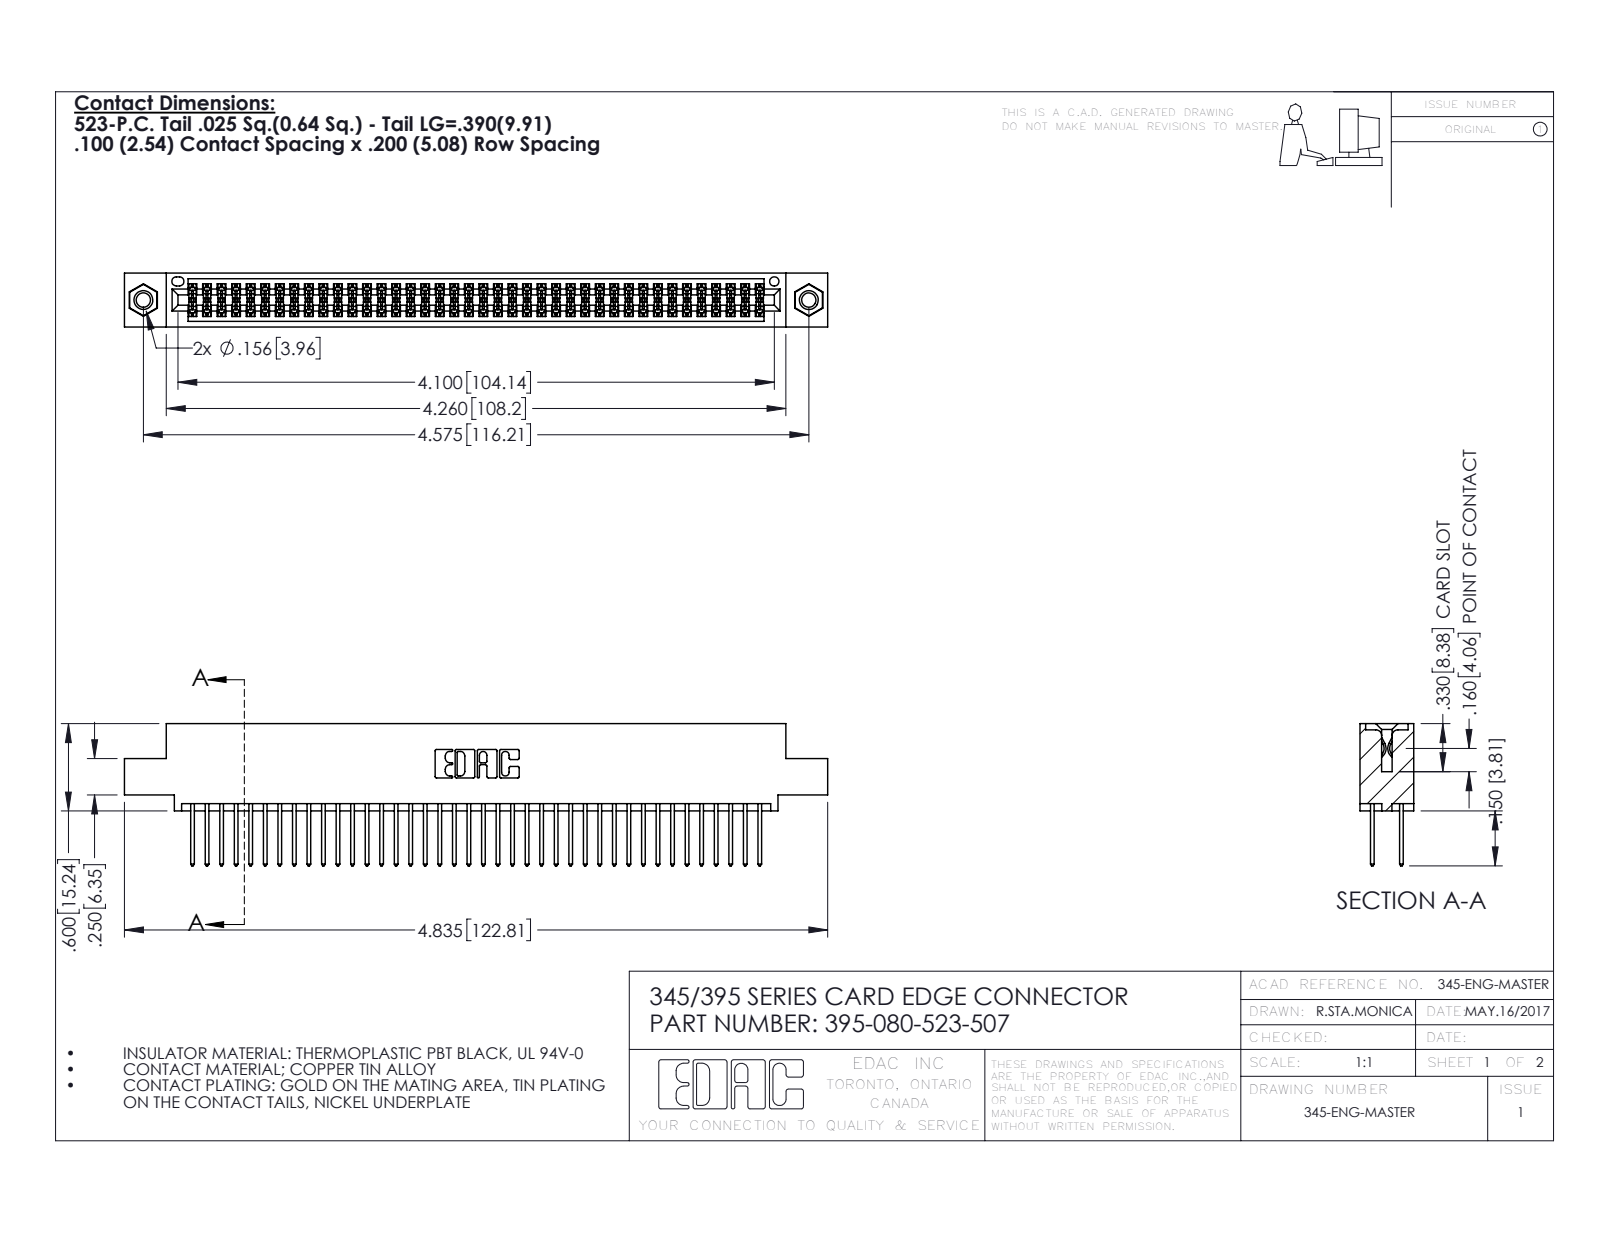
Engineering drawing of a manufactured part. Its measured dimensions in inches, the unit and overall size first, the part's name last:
Units: inches
Overall size (bounding box): 4.835 × 0.977 × 0.37
Round holes (diameter × count): ⌀0.098 ×2, ⌀0.125 ×2, ⌀0.156 ×2, ⌀0.064 ×1
Round bosses / shafts (diameter × count): ⌀0.155 ×2
Partial cylindrical surfaces — rounded edges, fillets, slot ends (radius × count): R0.006 ×120, R0.01 ×80, R0.01 ×22, R0.007 ×6, R0.031 ×6, R0.026 ×3, R0.014 ×2, R0.019 ×2
Main face-to-face distances: 0.072, 0.298, 0.2, 0.098, 0.272, 0.025, 0.37, 0.225, 0.175, 0.149
Hole centre spacings: 0.27, 4.339, 4.575
Volume: 0.732 in³ · Surface area: 28.73 in²
Bodies: 83 solids, 4190 faces (2756 planar, 1418 cylindrical, 16 other)
Part name (STEP PRODUCT): 345-250-001_345-250-005-103; 345-292-001_345-293-123; 395-080-523-507; 345 Part_0.110 Offset - 0.156 Dia-TI
STEP written by: SolidWorks 2016 (CONFIG_CONTROL_DESIGN)
